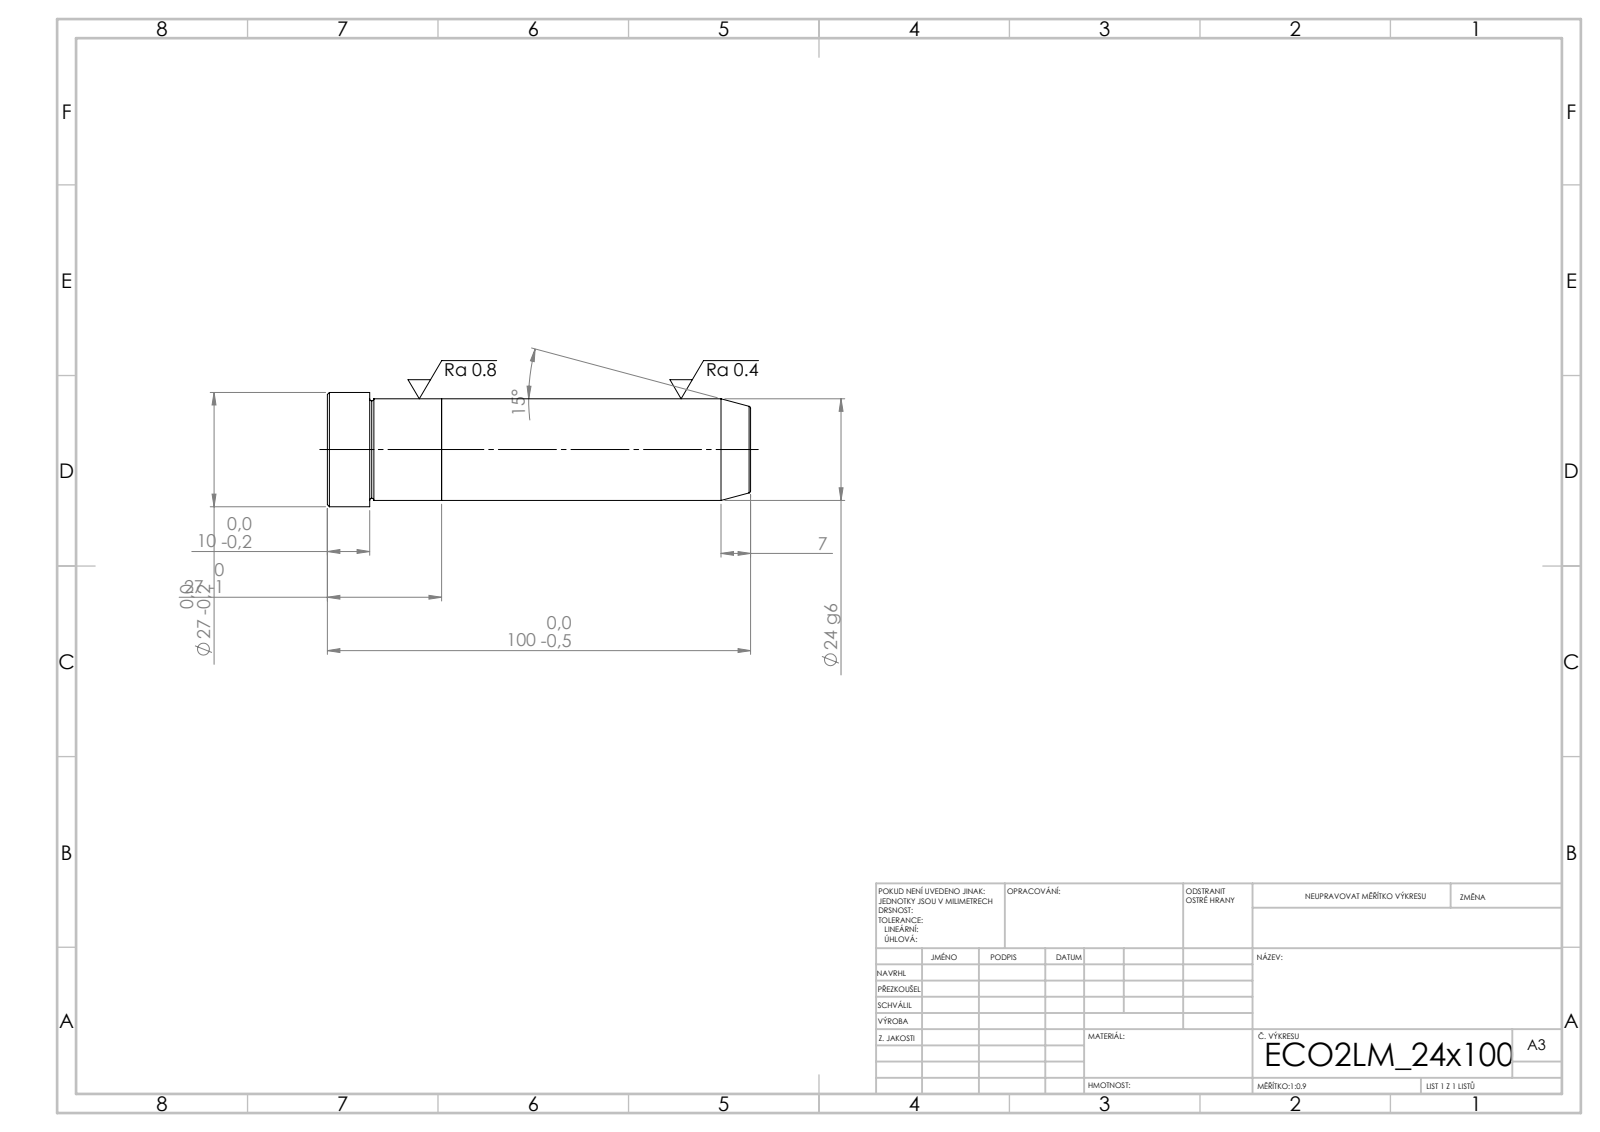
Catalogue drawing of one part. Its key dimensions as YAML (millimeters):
step_written_by: "SolidWorks 2019 (CONFIG_CONTROL_DESIGN)"
units: millimeters
bodies: {solids: 2, faces: 21, planar: 5, cylindrical: 6, other: 10}
overall_size: [100, 27, 27]
volume: 45930
surface_area: 9537
round_bosses_or_shafts:
  - {diameter: 27, count: 1}
  - {diameter: 24, count: 1}
face_to_face_distances: [27, 73, 100, 90, 17, 10]
